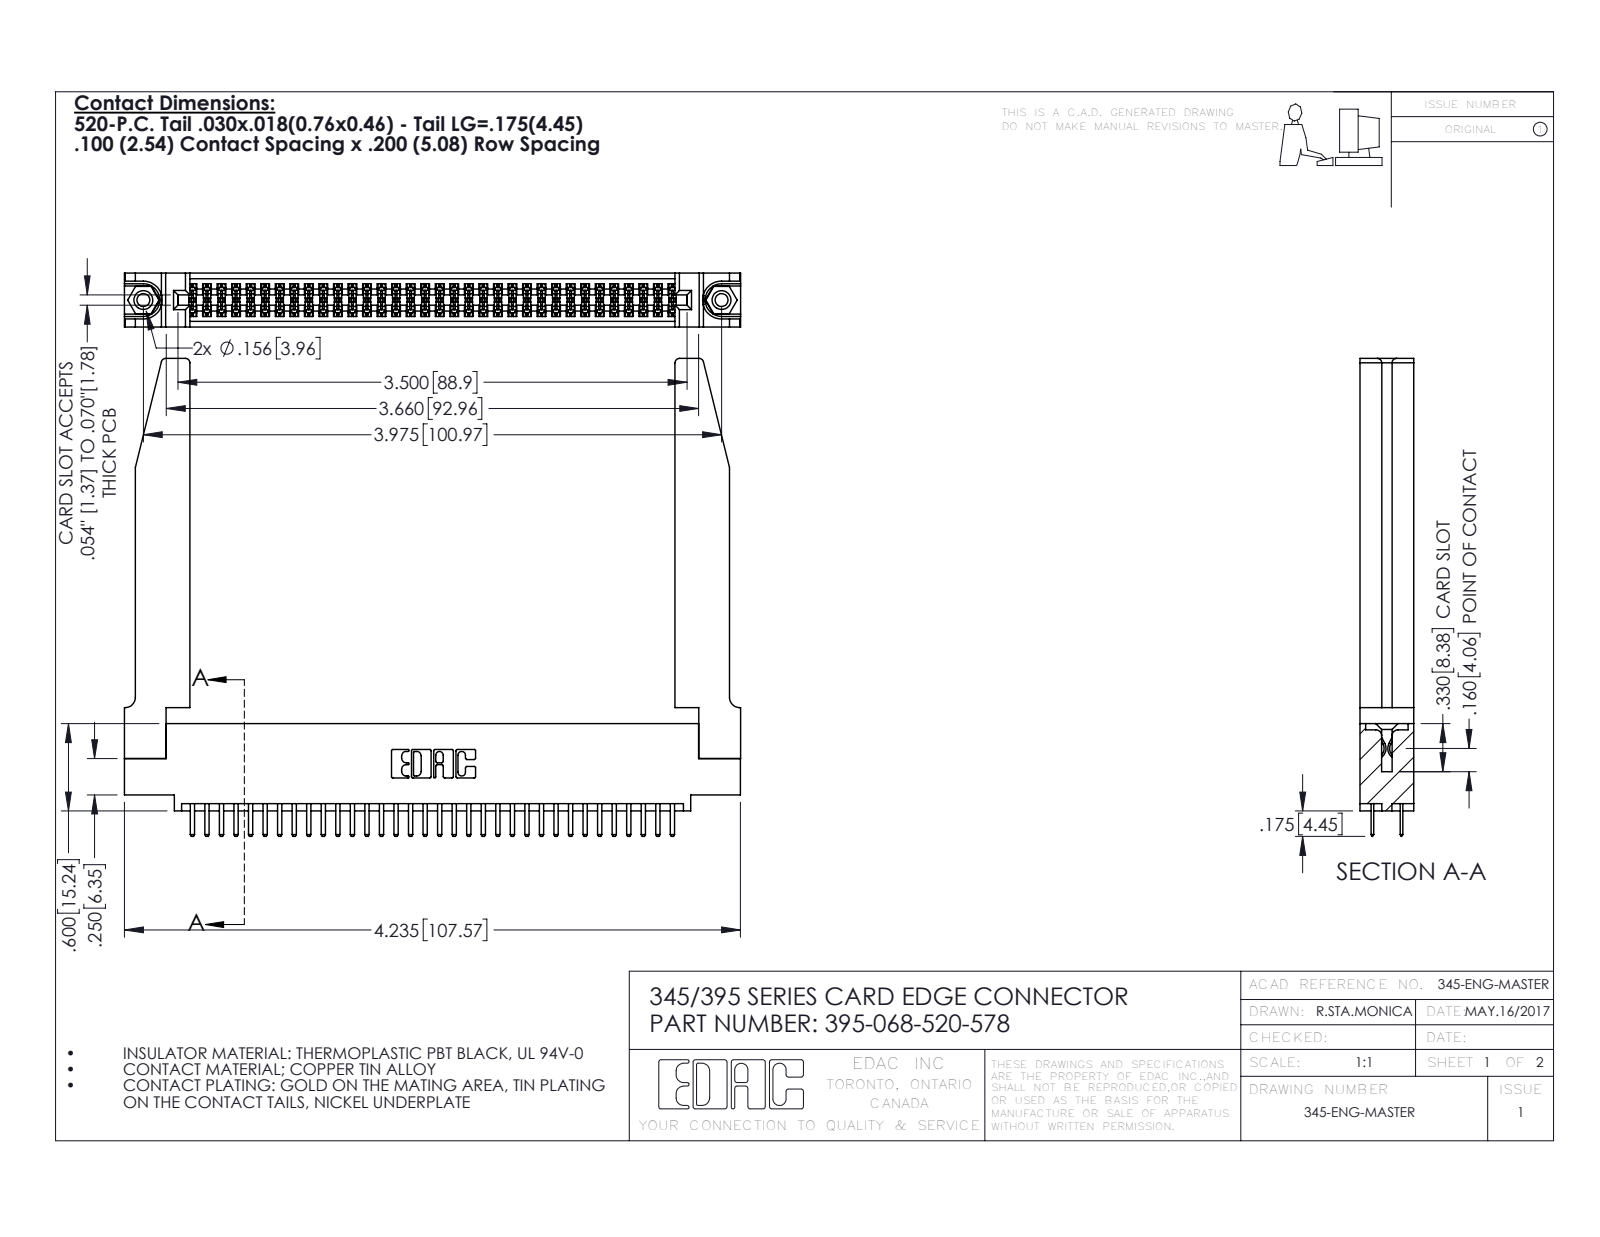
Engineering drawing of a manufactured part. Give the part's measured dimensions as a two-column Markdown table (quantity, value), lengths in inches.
| quantity | value |
| --- | --- |
| part name | 395-068-520-578; 345 Part_0.110 Offset - 0.156 Dia-TH; 345-220-078_345-220-078; 345-292-001_345-293-120 (+1 more) |
| STEP written by | SolidWorks 2016 (CONFIG_CONTROL_DESIGN) |
| units | inches |
| bodies | 73 solids, 4036 faces (2606 planar, 1378 cylindrical, 52 other) |
| overall size | 4.236 × 3.285 × 0.37 |
| volume | 1.101 in³ |
| surface area | 33.94 in² |
| round holes (diameter × count) | 0.089 × 2, 0.125 × 2, 0.156 × 2, 0.064 × 1 |
| round bosses / shafts (diameter × count) | 0.155 × 2 |
| partial cylindrical surfaces (radius × count) | 0.006 × 102, 0.01 × 72, 0.01 × 22, 0.03 × 8, 0.007 × 6, 0.031 × 6, 0.026 × 3, 0.014 × 2 |
| main face-to-face distances | 0.37, 0.072, 0.298, 0.2, 0.098, 0.272, 0.025, 0.225, 0.022, 0.175 |
| hole center spacings | 0.27, 3.74, 3.975 |
